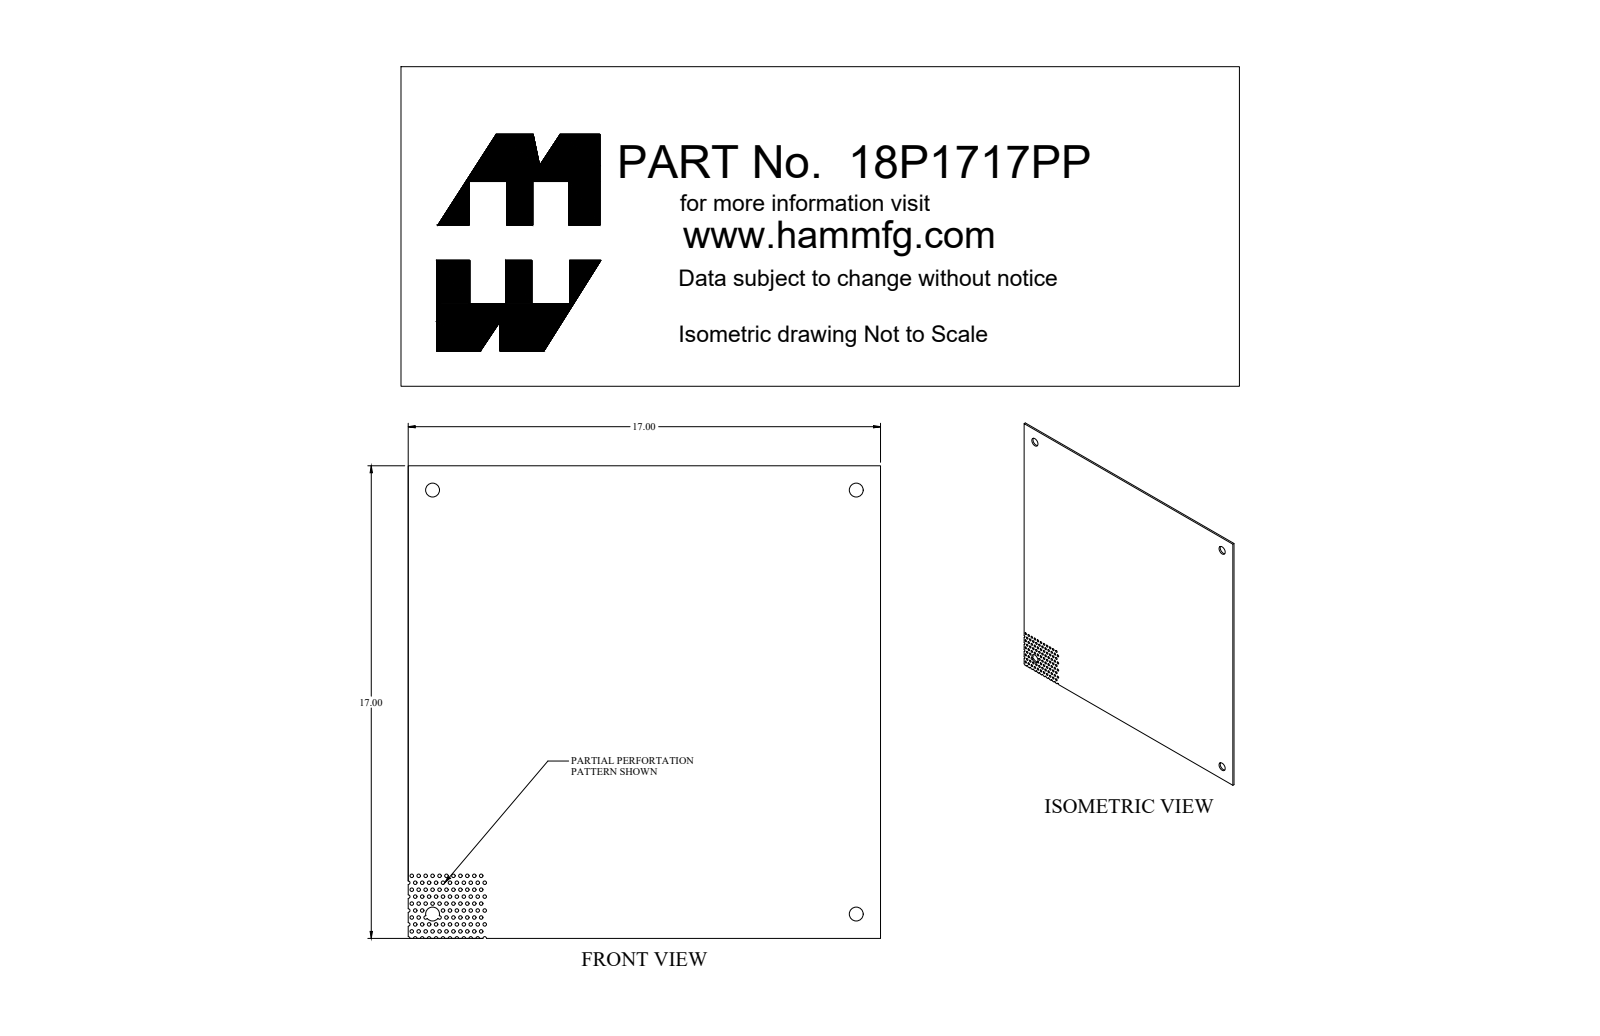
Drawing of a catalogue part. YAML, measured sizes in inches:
part_name: "18P1717PP_Default"
step_written_by: "SolidWorks 2018 (CONFIG_CONTROL_DESIGN)"
units: inches
bodies: {solids: 1, faces: 251, planar: 21, cylindrical: 230, other: 0}
overall_size: [17, 17, 0.057]
volume: 16.36
surface_area: 580.3
round_holes:
  - {diameter: 0.125, count: 94}
  - {diameter: 0.5, count: 4}
partial_cylinders:
  - {radius: 0.062, count: 18}
face_to_face_distances: [0.057, 17]
hole_center_spacings: [0.28, 0.5, 0.25, 0.673, 0.451, 0.75, 0.91, 1.153]
